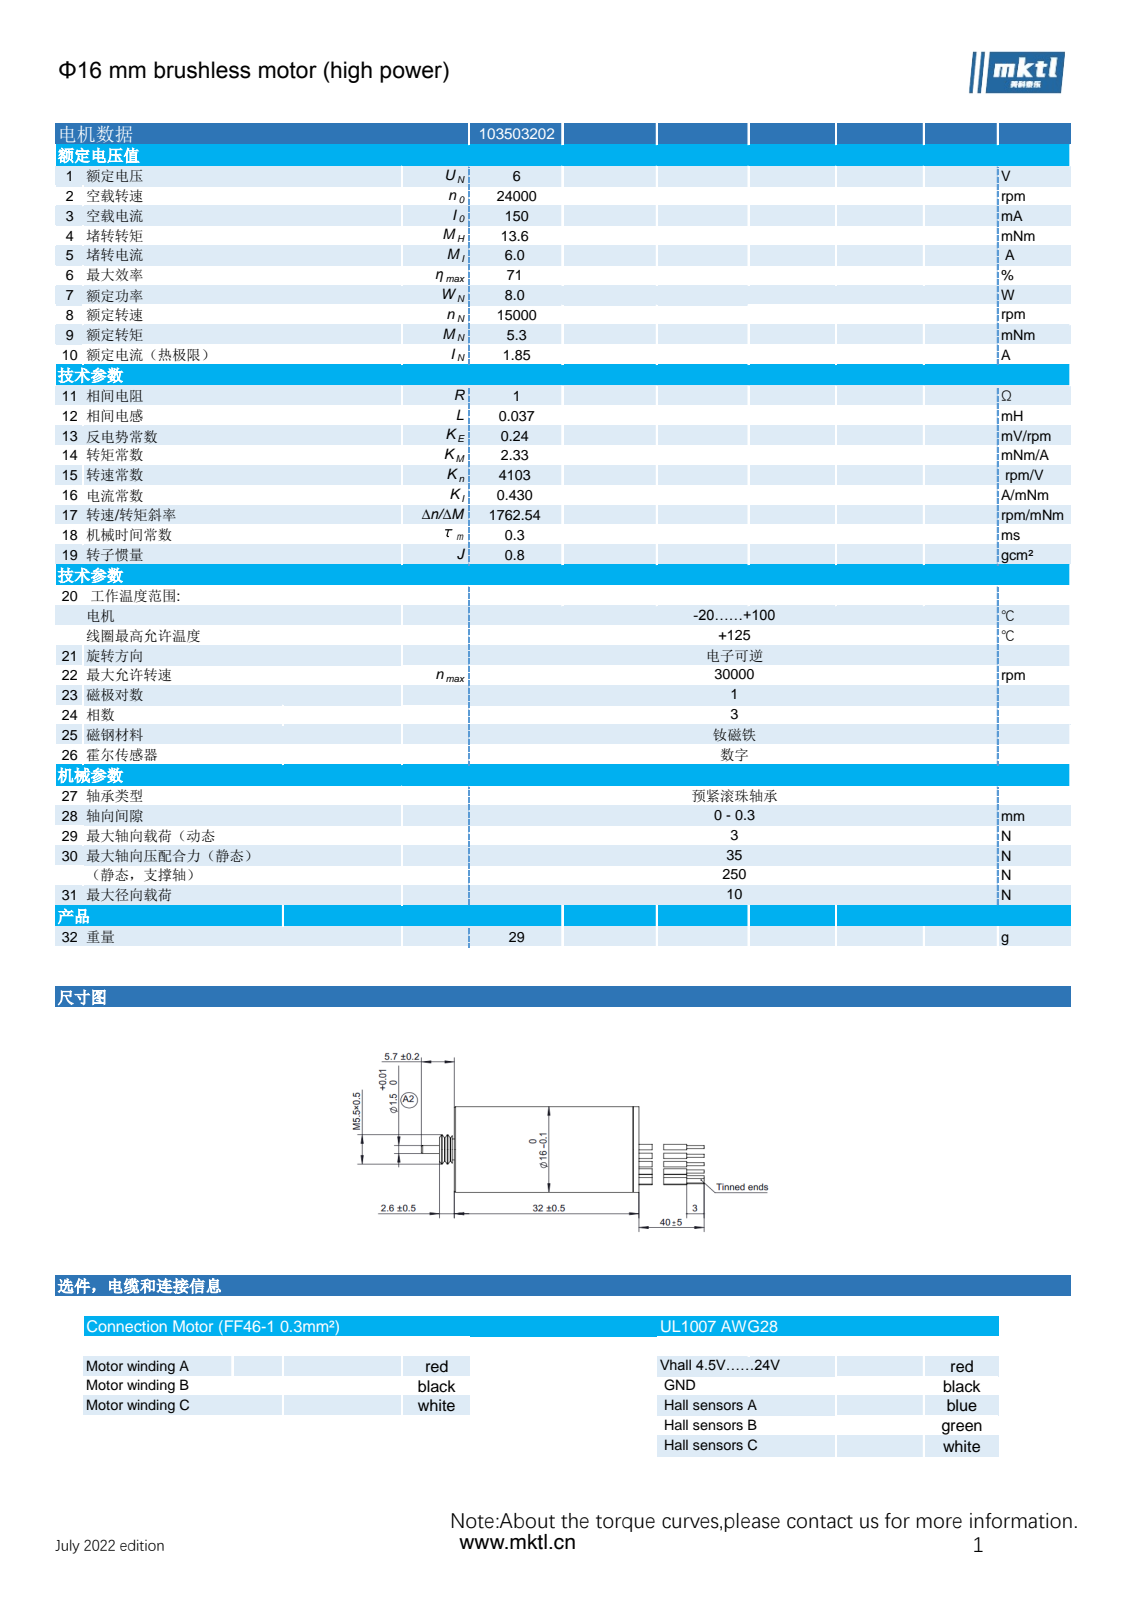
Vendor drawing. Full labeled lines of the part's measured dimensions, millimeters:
Part name (STEP PRODUCT): 103503202
STEP written by: SolidWorks 2025 (AUTOMOTIVE_DESIGN)
Units: millimetres
Bodies: 130 solids, 1001 faces (341 planar, 595 cylindrical, 65 other)
Overall size (bounding box): 49 × 16 × 16
Volume: 5 725 mm³ · Surface area: 23 053 mm²
Round holes (diameter × count): ⌀1.2 ×8, ⌀0.6 ×5, ⌀0.8 ×3, ⌀1.1 ×3, ⌀1.4 ×3, ⌀3 ×1, ⌀3.3 ×1, ⌀3.5 ×1, ⌀4.5 ×1, ⌀7 ×1, ⌀8 ×1, ⌀8.1 ×1
Round bosses / shafts (diameter × count): ⌀1 ×5, ⌀1.2 ×3, ⌀0.8 ×3, ⌀0.3 ×3, ⌀16 ×1, ⌀15 ×1, ⌀14.9 ×1, ⌀14.5 ×1
Partial cylindrical surfaces — rounded edges, fillets, slot ends (radius × count): R0.55 ×2, R0.85 ×2, R5.15 ×1, R5.65 ×1, R6.5 ×1, R6.85 ×1, R7.2 ×1
Main face-to-face distances: 0.4, 0.6, 1, 0.8, 1.2, 1.4, 1.6, 1.8, 2, 2.2
Hole centre spacings: 1.64, 3.25, 6, 6.28, 6.29, 6.8, 11.87, 1.42
